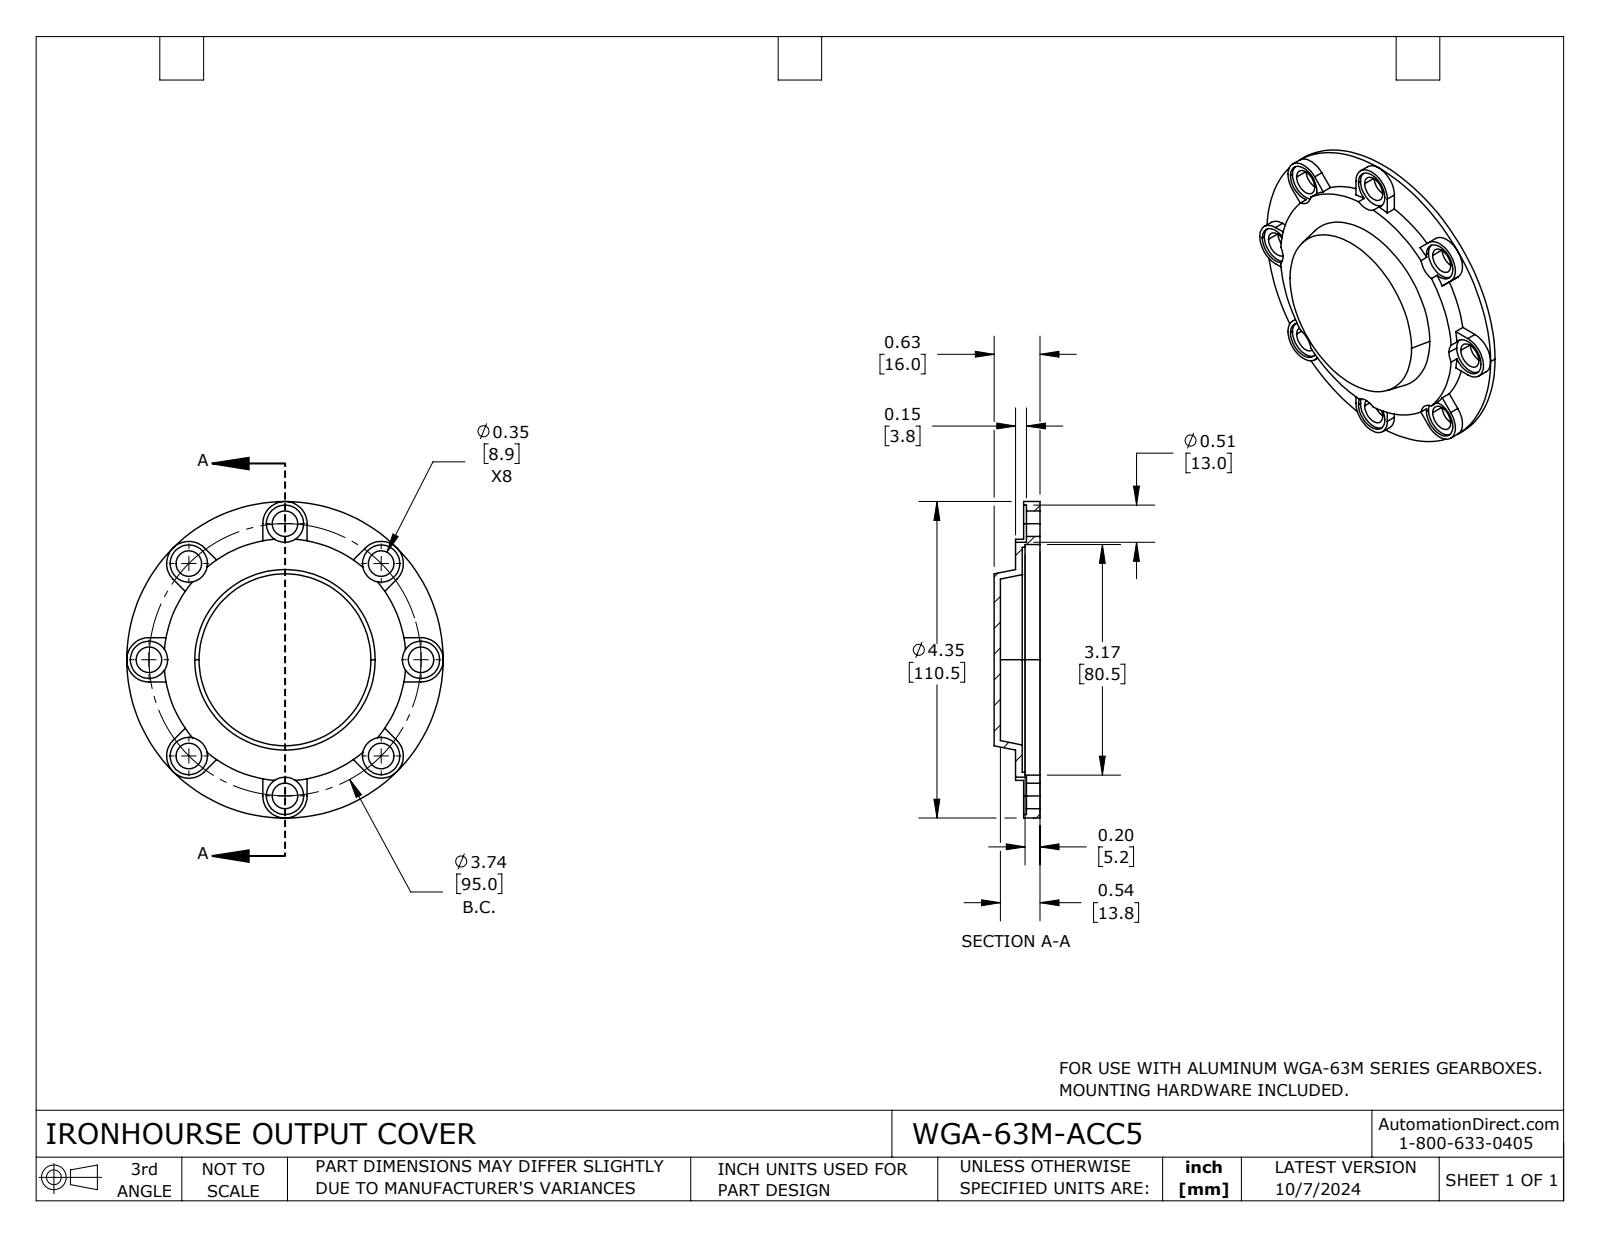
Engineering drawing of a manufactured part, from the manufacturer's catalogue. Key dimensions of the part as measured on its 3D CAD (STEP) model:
Part name (STEP PRODUCT): WGA-63M-ACC5
STEP written by: SolidWorks 2023 (CONFIG_CONTROL_DESIGN)
Units: millimetres
Bodies: 1 solid, 107 faces (46 planar, 57 cylindrical, 4 other)
Overall size (bounding box): 110.5 × 110.5 × 16
Volume: 28 867 mm³ · Surface area: 26 471 mm²
Round holes (diameter × count): ⌀8.9 ×8, ⌀13 ×8, ⌀78.5 ×1, ⌀80.5 ×1
Round bosses / shafts (diameter × count): ⌀110.5 ×1
Partial cylindrical surfaces — rounded edges, fillets, slot ends (radius × count): R7.75 ×8, R42.25 ×1
Main face-to-face distances: 2.2, 13.8, 16, 11.6, 7.5, 5.3, 6.3, 8.5, 9.8, 7.6
Hole centre spacings: 36.36, 47.5, 67.18, 87.77, 95, 95.01
